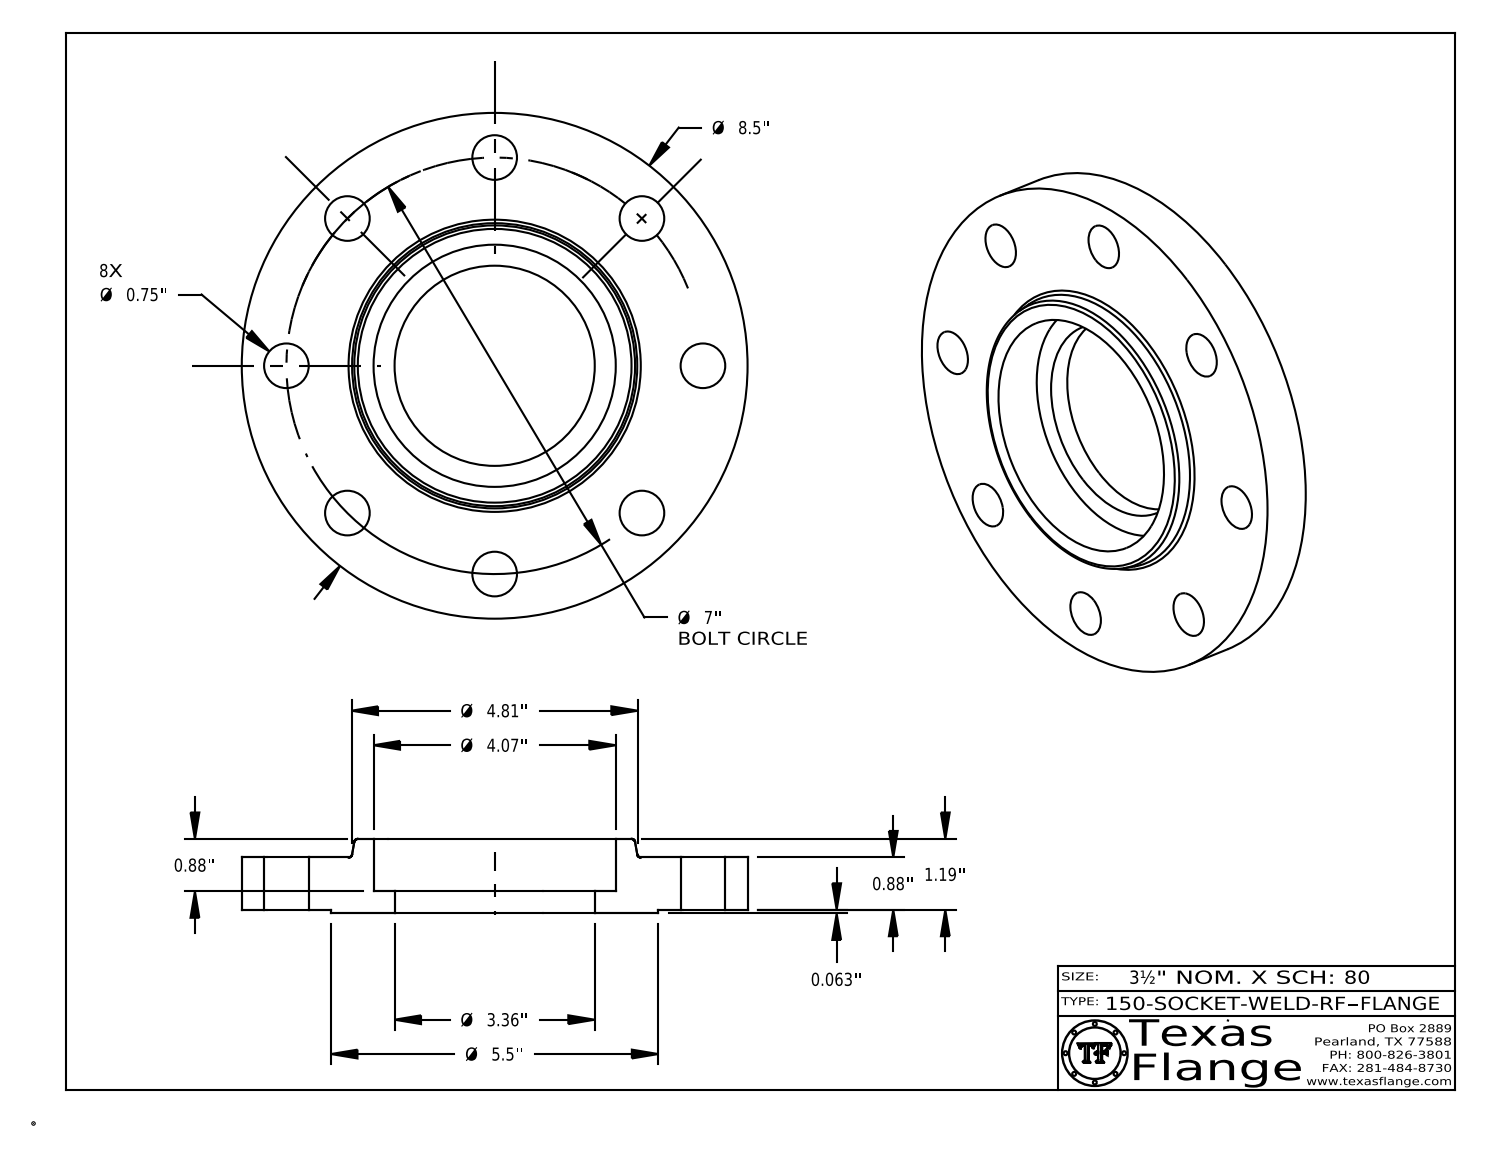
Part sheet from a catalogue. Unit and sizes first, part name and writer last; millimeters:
Units: millimetres
Overall size (bounding box): 215.9 × 215.9 × 31.8
Round holes (diameter × count): ⌀19.1 ×8, ⌀12.6 ×1, ⌀85.4 ×1, ⌀103.4 ×1
Round bosses / shafts (diameter × count): ⌀0.8 ×8, ⌀215.9 ×1, ⌀139.7 ×1, ⌀9.9 ×1
Main face-to-face distances: 22.4, 1.6, 24, 9.4, 7.9, 14.5, 31.8, 30.2, 22.4, 7.9
Hole centre spacings: 88.9, 68, 125.7, 164.3, 34.7, 98.8, 147.8, 174.4
Volume: 640 100 mm³ · Surface area: 95 810 mm²
Bodies: 1 solid, 420 faces (370 planar, 44 cylindrical, 6 other)
Part name (STEP PRODUCT): 150-SOCKET-WELD-RF
STEP written by: CATIA V5 STEP AP214 (AUTOMOTIVE_DESIGN)
